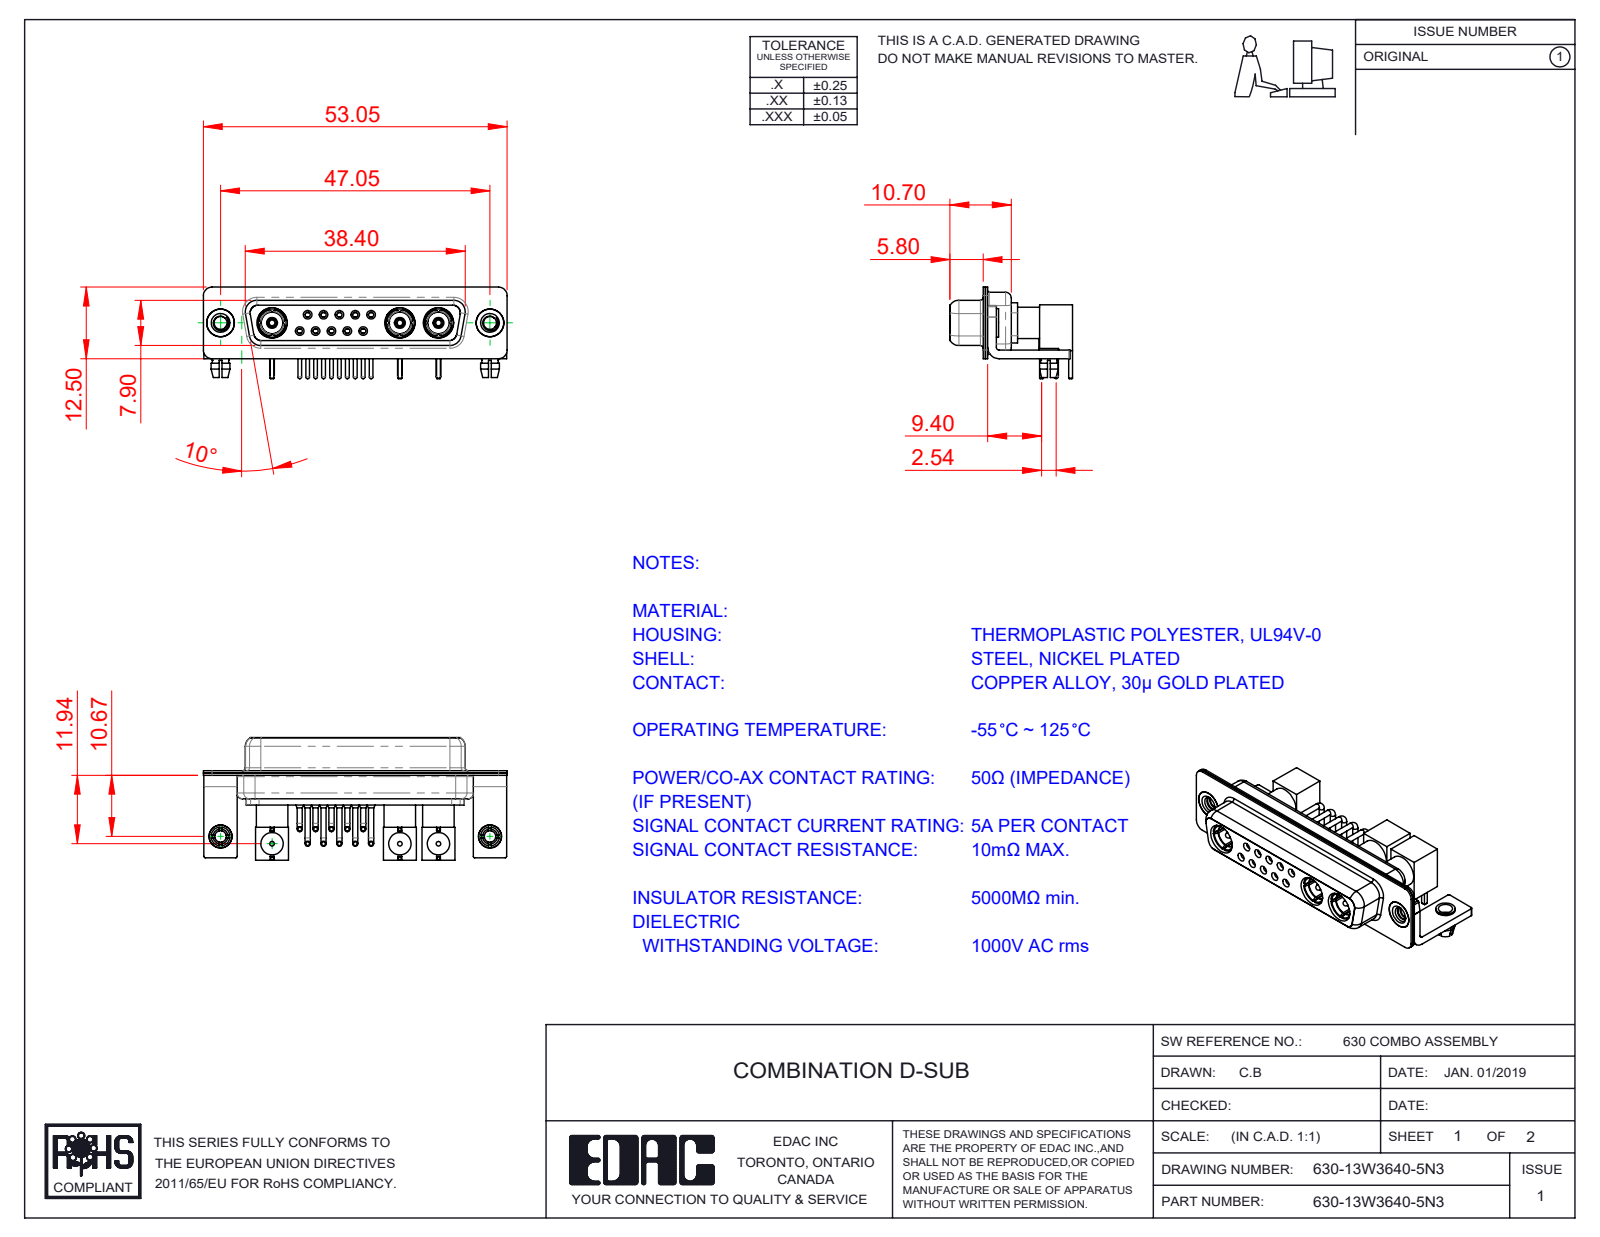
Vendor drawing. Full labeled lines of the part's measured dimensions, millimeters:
Part name (STEP PRODUCT): 630Combo Contact Row 2; Co-Ax Plug_RA PC Tail; 630Combo Threaded Rivet_3; Co-Ax Plug Assy_RA (+8 more)
STEP written by: SolidWorks 2020 (CONFIG_CONTROL_DESIGN)
Units: millimetres
Bodies: 37 solids, 1445 faces (486 planar, 612 cylindrical, 347 other)
Overall size (bounding box): 53.05 × 21.41 × 16
Volume: 4 826 mm³ · Surface area: 11 681 mm²
Round holes (diameter × count): ⌀1.1 ×13, ⌀1.5 ×13, ⌀2 ×12, ⌀0.9 ×10, ⌀1.6 ×5, ⌀1.7 ×5, ⌀4.85 ×5, ⌀0.8 ×3, ⌀2.83 ×3, ⌀3.1 ×3, ⌀3.3 ×3, ⌀3.9 ×3
Round bosses / shafts (diameter × count): ⌀0.9 ×10, ⌀0.65 ×10, ⌀5 ×5, ⌀4 ×5, ⌀2.9 ×5, ⌀1.6 ×5, ⌀5.5 ×3, ⌀5.2 ×3
Partial cylindrical surfaces — rounded edges, fillets, slot ends (radius × count): R0.25 ×16, R1.5 ×16, R2 ×13, R1.35 ×8, R1.6 ×8, R0.5 ×5, R0.6 ×4, R0.65 ×4
Main face-to-face distances: 0.4, 1.4, 1.8, 0.45, 8.45, 0.8, 8.9, 1.35, 6.2, 7.05
Hole centre spacings: 3.16, 2.77, 5.54, 5.03, 5.04, 8.31, 7.48, 6.74
